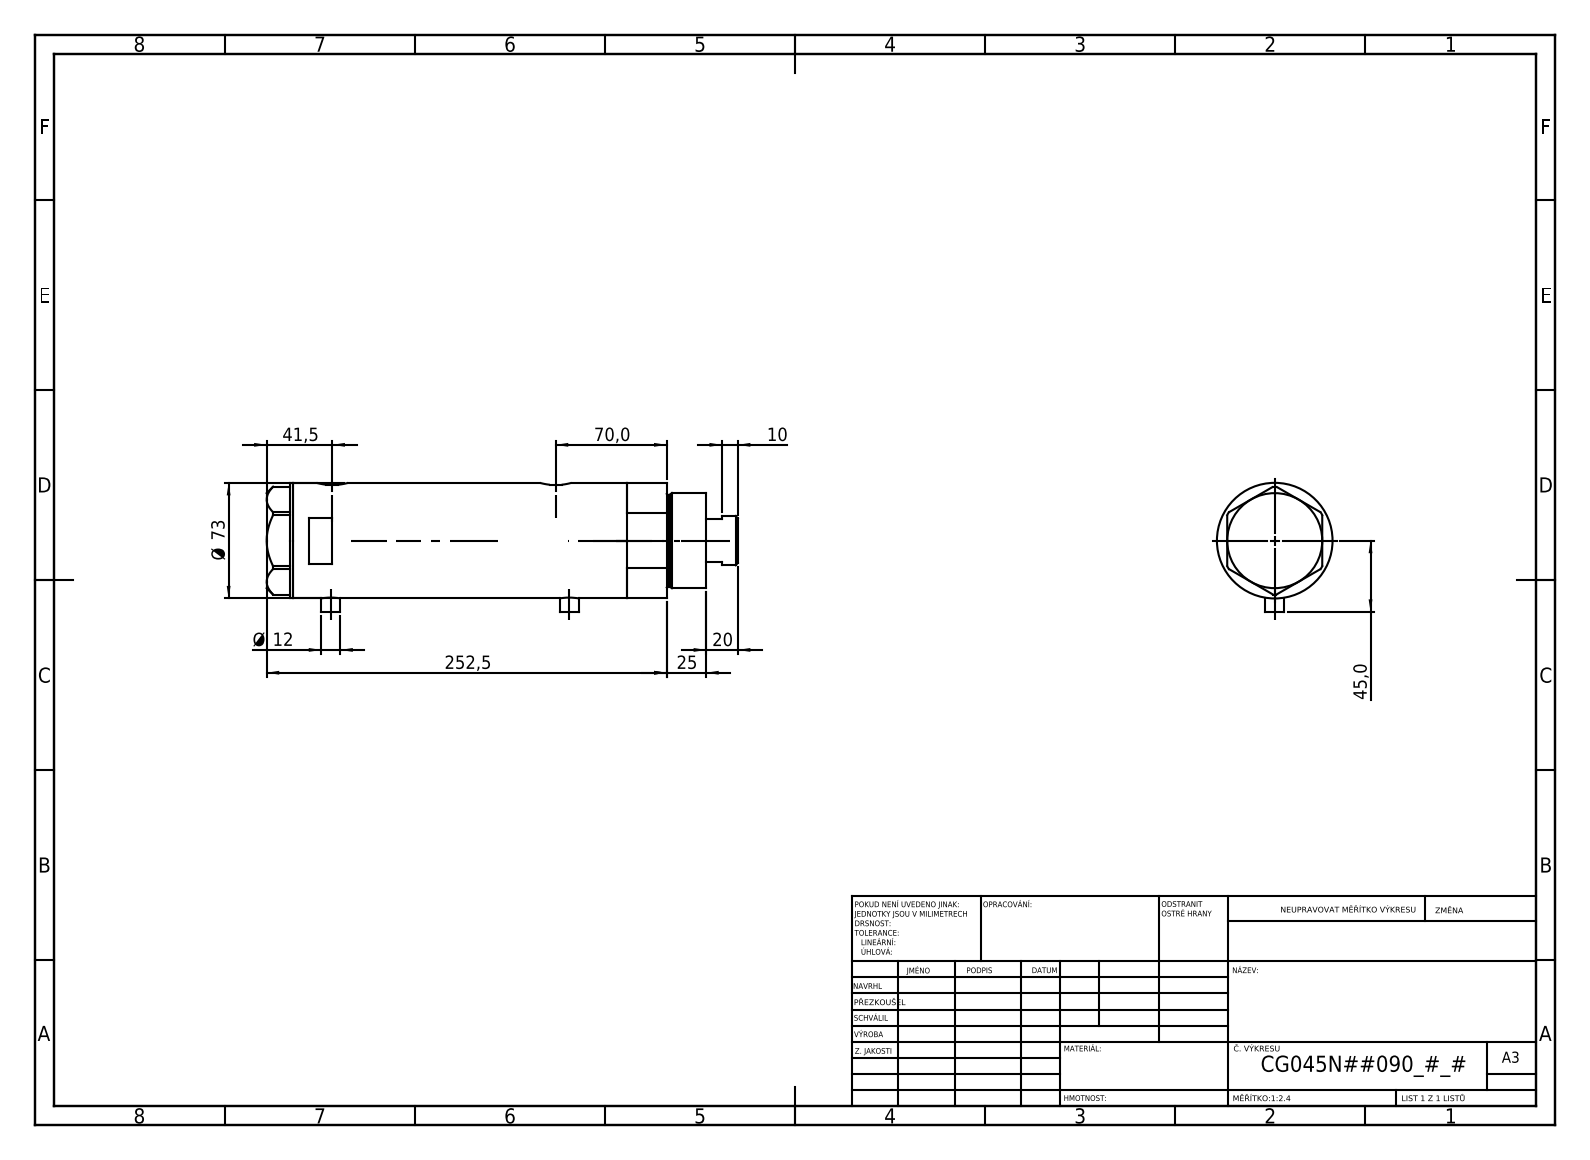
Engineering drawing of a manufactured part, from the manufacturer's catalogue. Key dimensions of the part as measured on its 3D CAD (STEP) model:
Part name (STEP PRODUCT): V270CG_FRONT; V270CG_BACK; V270CG_VC; V270CG_MIDDLE
STEP written by: SolidWorks 2019 (CONFIG_CONTROL_DESIGN)
Units: millimetres
Bodies: 4 solids, 120 faces (49 planar, 51 cylindrical, 20 other)
Overall size (bounding box): 297.5 × 81.5 × 73
Volume: 1 043 000 mm³ · Surface area: 170 361 mm²
Round holes (diameter × count): ⌀12.5 ×2, ⌀13.16 ×2, ⌀10.5 ×1, ⌀32 ×1, ⌀33.5 ×1, ⌀45 ×1, ⌀48 ×1, ⌀64 ×1
Round bosses / shafts (diameter × count): ⌀12 ×2, ⌀73 ×1, ⌀60 ×1, ⌀58 ×1, ⌀31 ×1
Partial cylindrical surfaces — rounded edges, fillets, slot ends (radius × count): R10 ×2
Main face-to-face distances: 166, 26, 140, 16.5, 42.5, 182.5, 2, 261, 277.5, 235
Hole centre spacings: 1, 8.5, 141, 142, 149.5, 150.5
